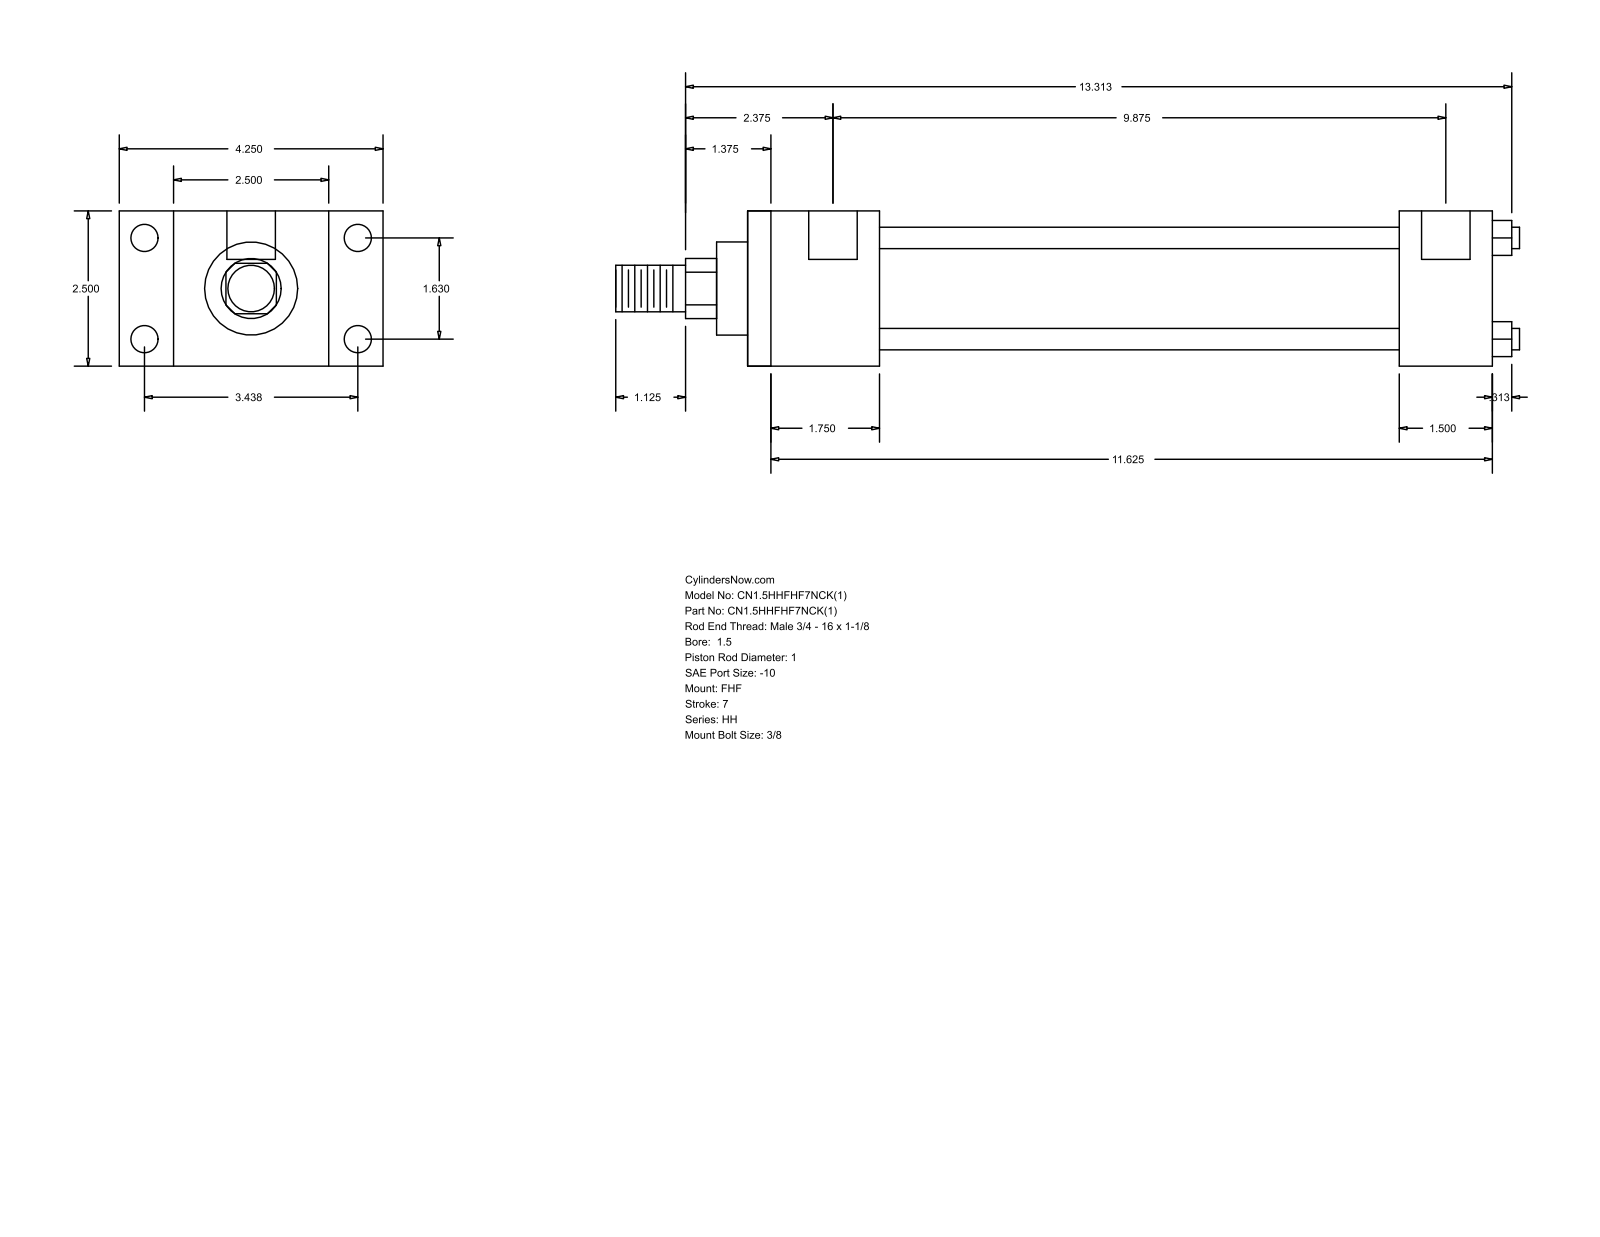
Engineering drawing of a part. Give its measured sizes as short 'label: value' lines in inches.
name: HH_FHF__0150_1
written by: GSSL Pune (CONFIG_CONTROL_DESIGN)
unit: in
bodies: 0 solids, 88 faces (60 planar, 28 cylindrical, 0 other)
size: 14.563 × 4.25 × 2.5
holes: 4× ⌀0.219, 4× ⌀0.438, 2× ⌀0.781
bosses: 4× ⌀0.345, 1× ⌀1.75, 1× ⌀1.5, 1× ⌀1, 1× ⌀0.75
rounds: 1× R0.484
face distances: 2.5, 0.875, 3.375, 2.125, 4.25, 12, 9.875, 1.5, 10.5, 8.375
hole spacings: 0.063, 1.63, 3.438, 3.805, 9.937, 10, 9.875
